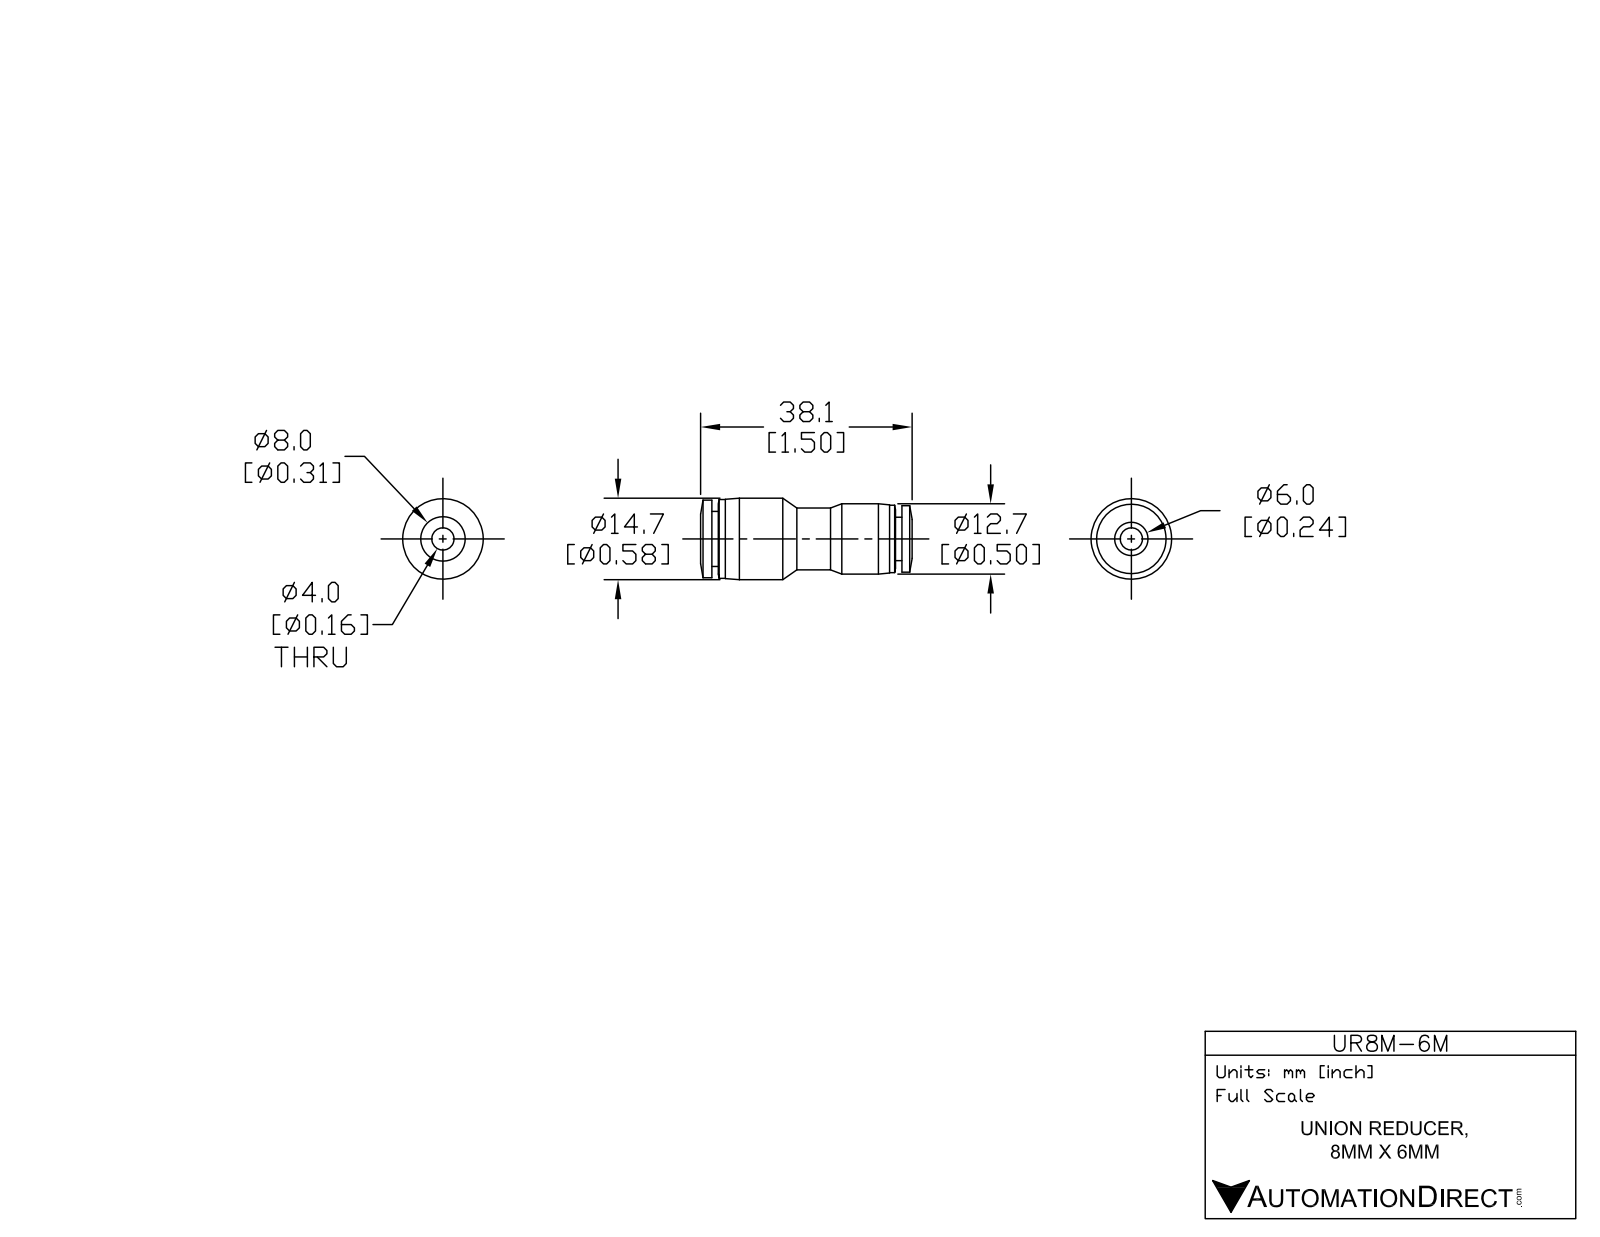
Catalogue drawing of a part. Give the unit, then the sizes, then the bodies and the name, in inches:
Units: inches
Overall size (bounding box): 1.48 × 0.571 × 0.571
Round holes (diameter × count): ⌀0.157 ×1, ⌀0.248 ×1, ⌀0.327 ×1
Round bosses / shafts (diameter × count): ⌀0.571 ×1, ⌀0.551 ×1, ⌀0.543 ×1, ⌀0.492 ×1, ⌀0.472 ×1, ⌀0.465 ×1, ⌀0.433 ×1, ⌀0.386 ×1
Main face-to-face distances: 0.045, 1.285, 1.331, 0.689, 0.596, 0.642, 0.644, 1.24, 0.575, 0.53
Volume: 0.195 in³ · Surface area: 4.384 in²
Bodies: 1 solid, 54 faces (10 planar, 24 cylindrical, 20 other)
Part name (STEP PRODUCT): UR8M-6M
STEP written by: SolidWorks 2015 (AUTOMOTIVE_DESIGN)
